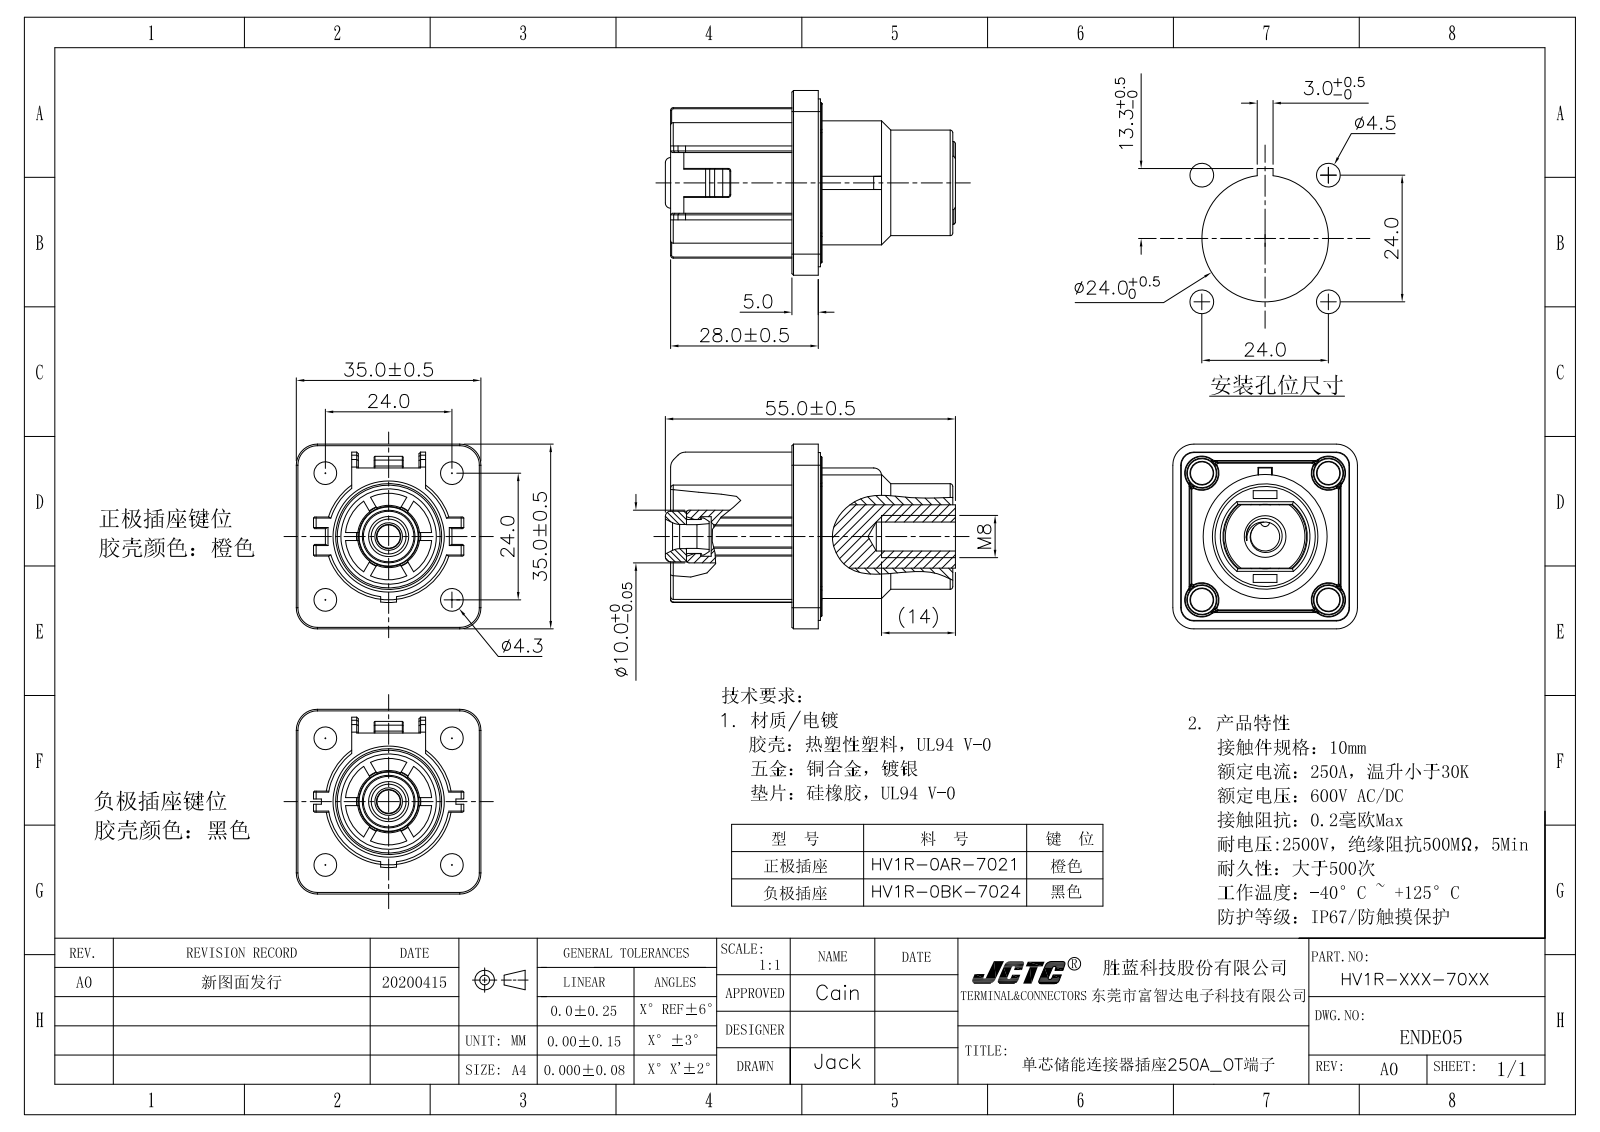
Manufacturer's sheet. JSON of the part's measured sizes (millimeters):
{"part_name": "F_BODY_243; DIANPIAO_31; F_JIAOSAI_57; F_ASM_329_ASM", "step_written_by": "CREO PARAMETRIC BY PTC INC, 2014500 (AUTOMOTIVE_DESIGN)", "units": "millimeters", "bodies": {"solids": 3, "faces": 865, "planar": 338, "cylindrical": 208, "other": 319}, "overall_size": [58, 35, 35], "volume_mm3": 20977, "surface_area_mm2": 18654, "round_holes": [[4.3, 4], [4.5, 4], [2, 1], [4.4, 1], [4.6, 1], [5.5, 1], [7.5, 1], [12.2, 1], [19.5, 1], [20.1, 1], [23.5, 1]], "round_bosses_or_shafts": [[28.3, 1], [20.3, 1], [20, 1], [12, 1], [11.4, 1], [10, 1], [9.8, 1], [9.6, 1]], "partial_cylinders_radius": [[1, 9], [0.15, 8], [0.15, 4], [0.19, 4], [0.19, 4], [0.25, 4], [0.5, 4], [2.4, 4]], "face_to_face_distances": [1.5, 5.4, 2, 28.4, 28.9, 23, 25, 3.9, 26.9, 10.5], "hole_center_spacings": [16.97, 24, 33.94]}
